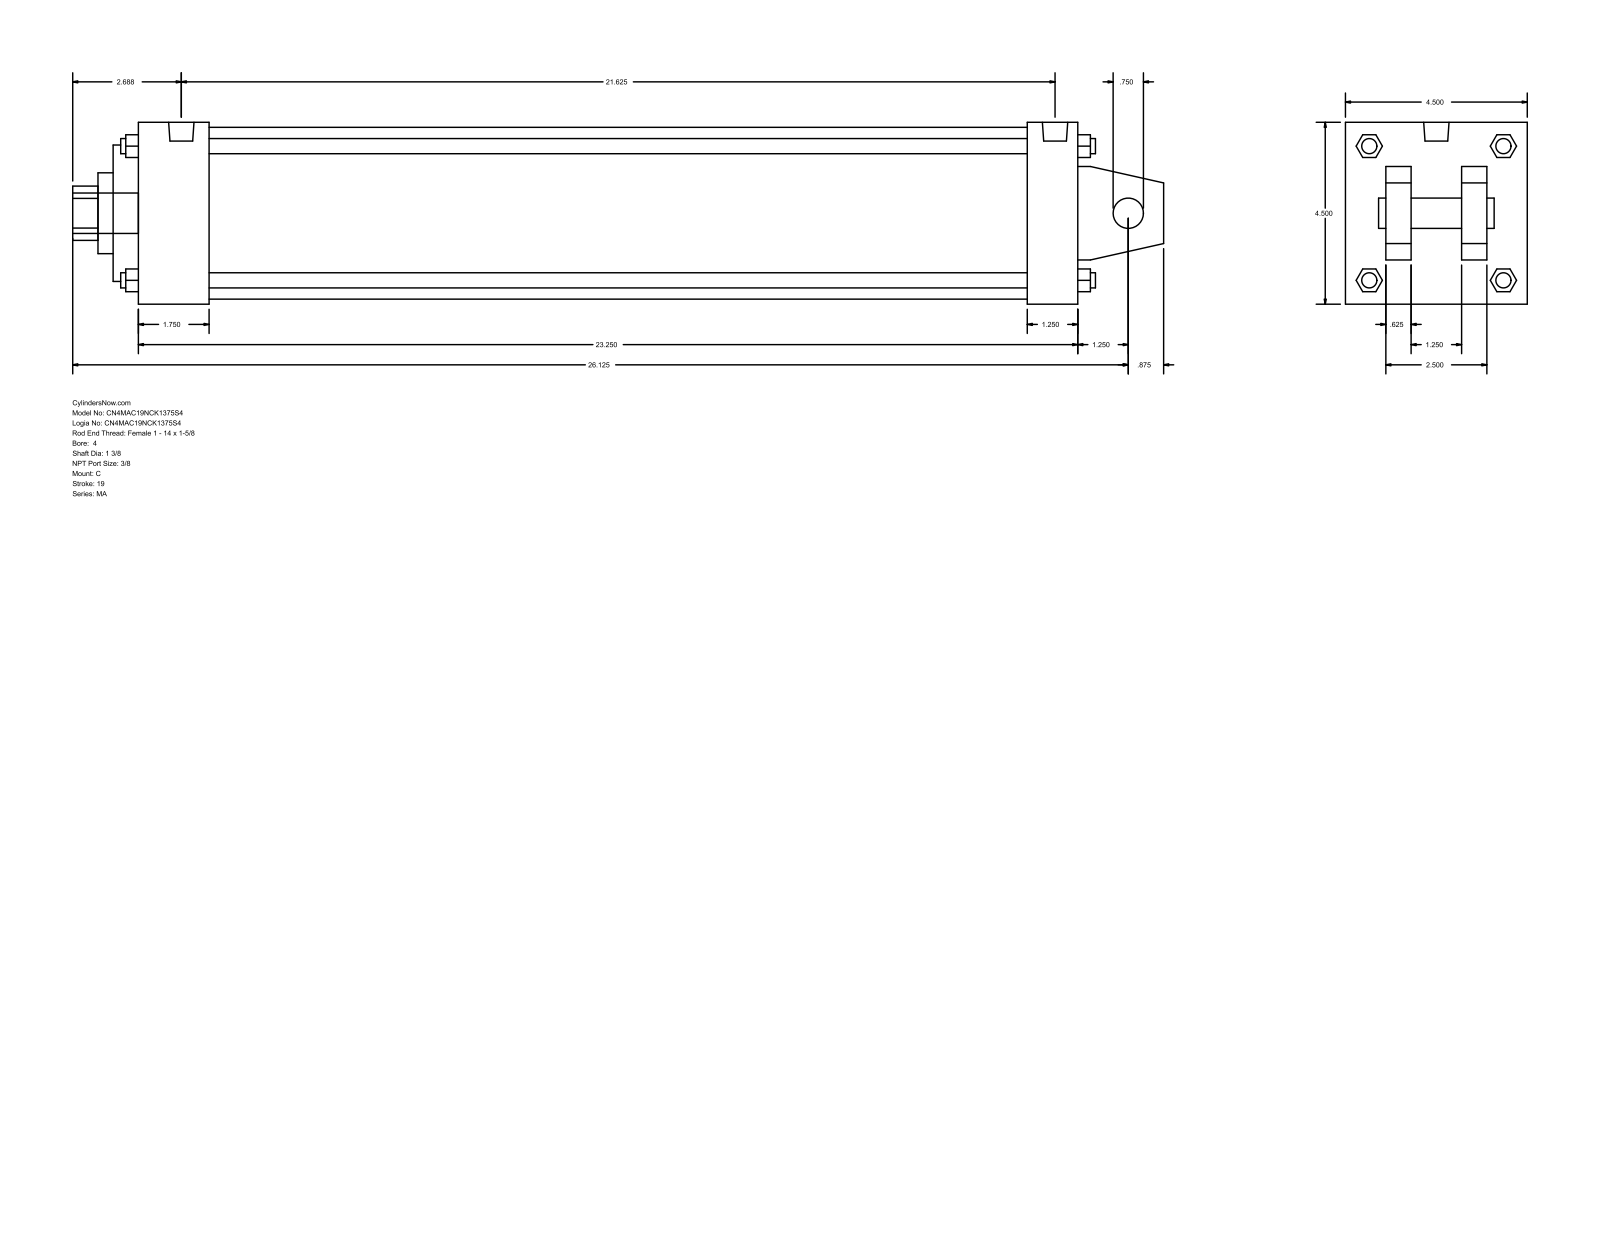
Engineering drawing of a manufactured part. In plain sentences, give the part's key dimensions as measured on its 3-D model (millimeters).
The part is named "MA_C__0400_1.375". Its 3-D file was written by "GSSL Pune (CONFIG_CONTROL_DESIGN)". It is 0 solids with 141 faces: 109 planar, 32 cylindrical and 0 other. Overall it measures 685.8 by 114.3 by 114.3 millimeters. Round holes: 1 of diameter 19.05, 1 of diameter 34.92, 1 of diameter 50.8, 1 of diameter 85.72, 1 of diameter 107.95. Round bosses or shafts: 4 of diameter 11.11, 4 of diameter 9.53, 2 of diameter 15.93, 1 of diameter 25.4. Partial cylindrical surfaces (rounded edges, fillets, slot ends): 1 of radius 17.06. The main face-to-face distances are 114.3, 15.87, 590.56, 73.03, 41.27, 25.4, 88.9, 47.63, 606.43, 574.68.
